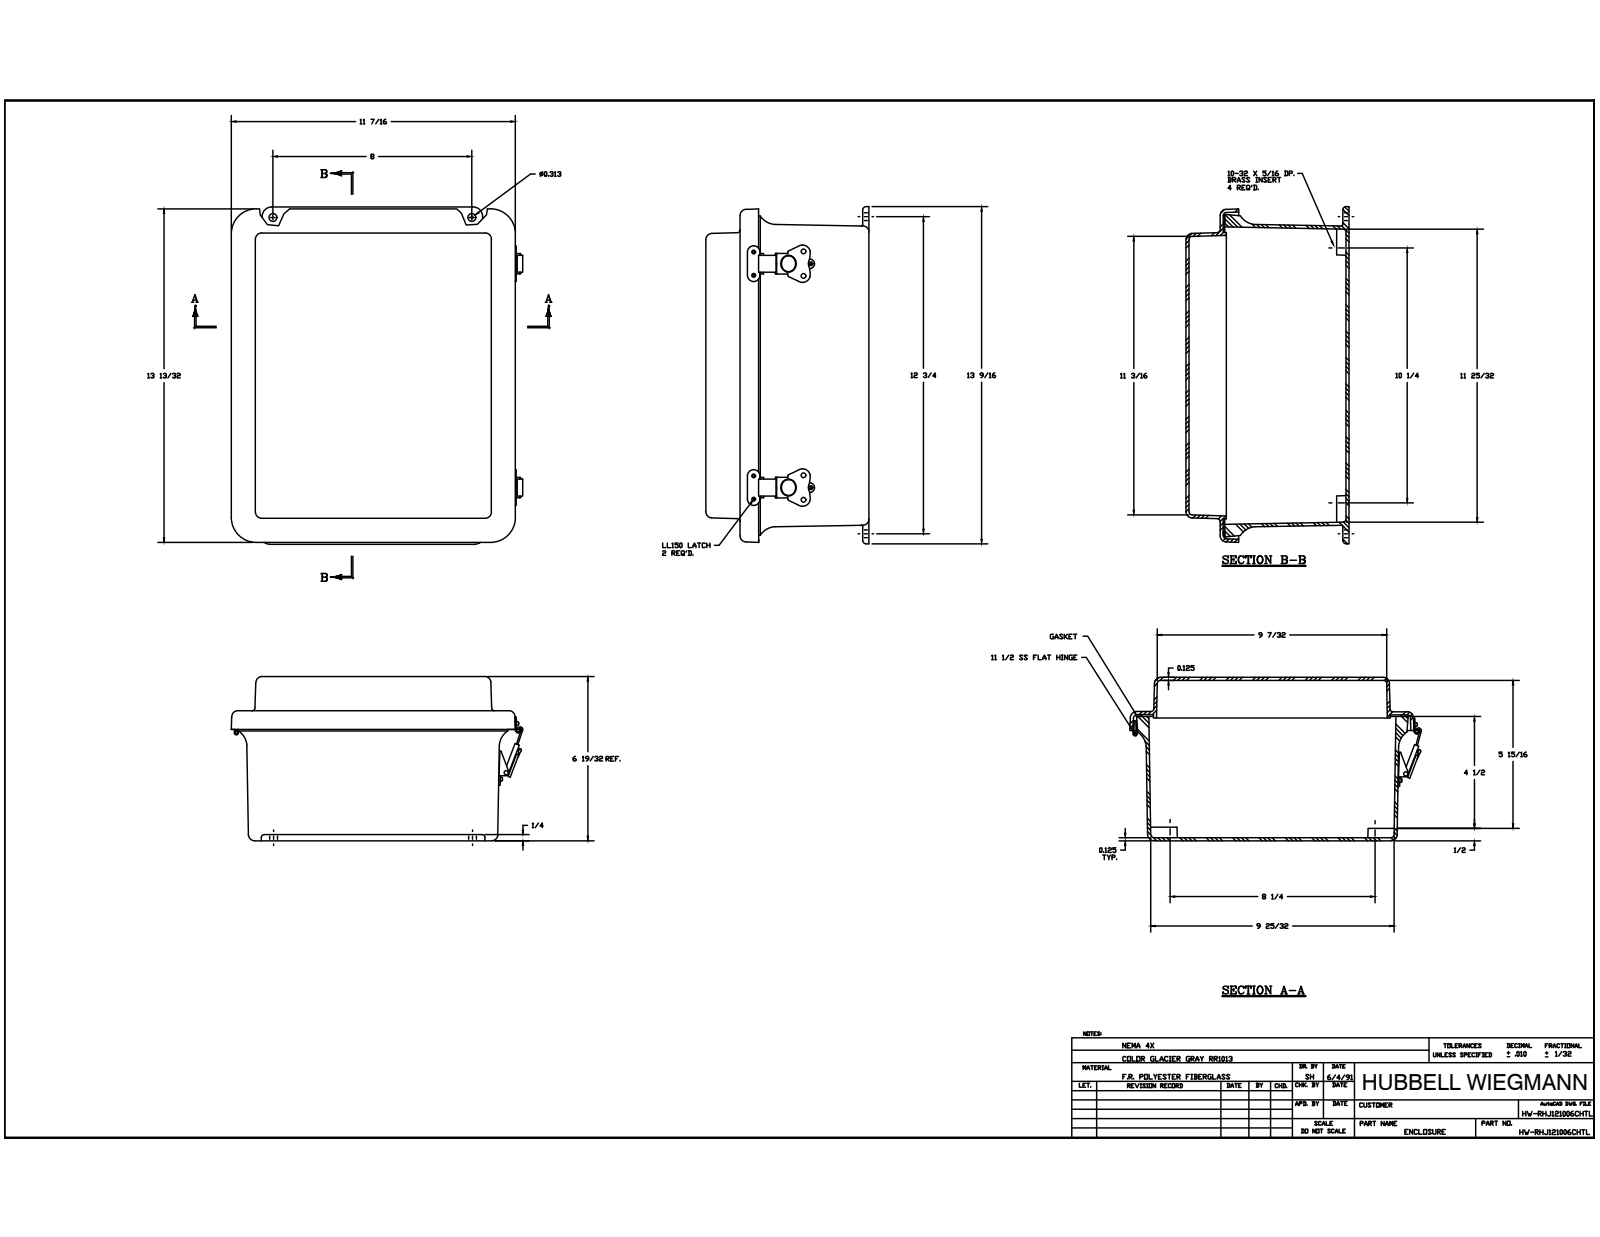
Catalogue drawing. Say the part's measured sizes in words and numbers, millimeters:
The part is named "J1210HL_7; RMINS45821P_181; RMINS45821P_182; RMINS45821P_183 (+8 more)". Its 3-D file was written by "Autodesk Inventor 2014 (AUTOMOTIVE_DESIGN)". It is 48 solids with 1212 faces: 536 planar, 461 cylindrical and 215 other. Overall it measures 344.49 by 294.9 by 167.33 millimeters. Its volume is 1 510 000 cubic millimeters and its surface area 842 713 square millimeters. Round holes: 16 of diameter 3.56, 8 of diameter 3.33, 5 of diameter 3.86, 4 of diameter 3.3, 4 of diameter 3.96, 4 of diameter 4.2, 4 of diameter 5, 4 of diameter 5.54, 2 of diameter 3, 2 of diameter 3.5, 2 of diameter 4.61, 2 of diameter 4.62. Round bosses or shafts: 16 of diameter 6.35, 16 of diameter 3.17, 4 of diameter 6.86, 2 of diameter 14.8, 2 of diameter 13.3, 2 of diameter 5.3, 2 of diameter 4.7, 2 of diameter 3.25. Partial cylindrical surfaces (rounded edges, fillets, slot ends): 20 of radius 0.79, 20 of radius 3.17, 19 of radius 2, 12 of radius 6.35, 8 of radius 0.95, 8 of radius 1, 8 of radius 1.15, 8 of radius 1.2. The main face-to-face distances are 3.18, 164.15, 167.33, 160.97, 128.92, 35.23, 125.74, 38.41, 132.1, 32.05. The hole center spacings are 228.6, 92.08, 17.79, 23.82, 34.24, 37.21, 55.59, 229.39.
